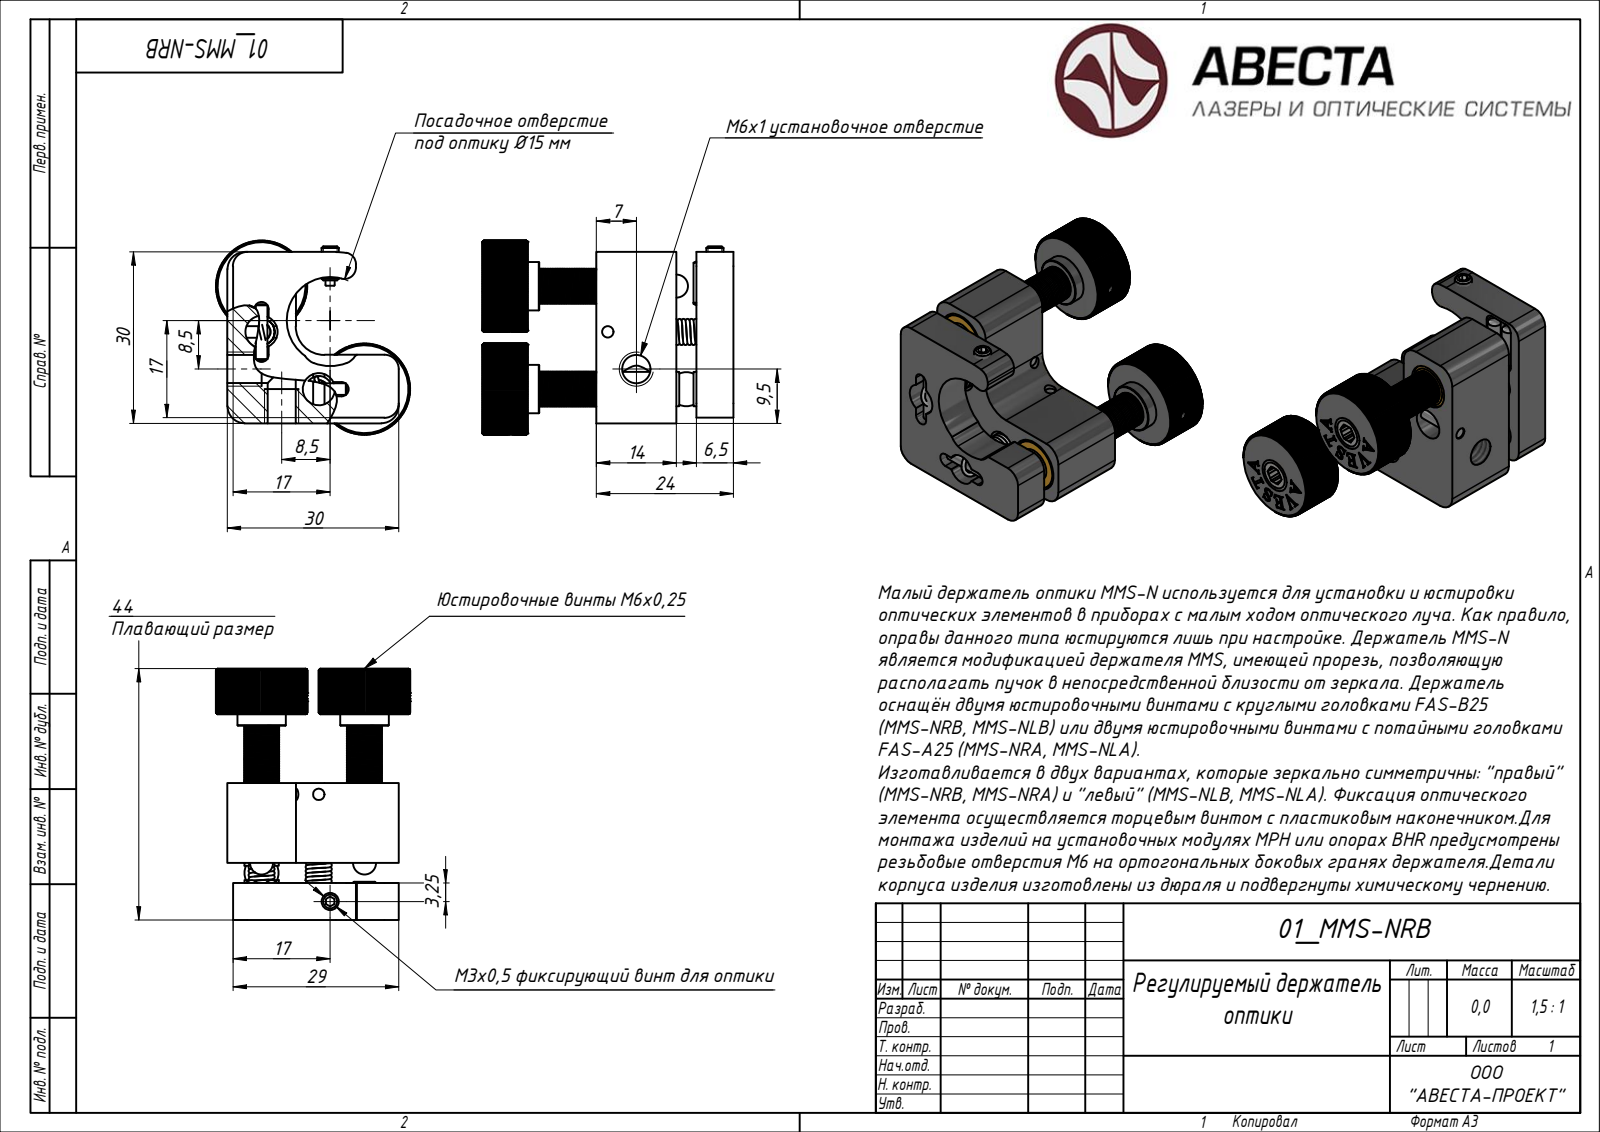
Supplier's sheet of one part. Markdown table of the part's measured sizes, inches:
| quantity | value |
| --- | --- |
| STEP written by | ST-DEVELOPER v15 (AUTOMOTIVE_DESIGN) |
| units | inches |
| bodies | 20 solids, 655 faces (294 planar, 0 cylindrical, 361 other) |
| overall size | 1.605 × 1.339 × 1.339 |
| volume | 0.858 in³ |
| surface area | 18.74 in² |
| main face-to-face distances | 0.394, 0.256, 0.945, 0.138, 0.472, 0.551, 0.039, 0.689, 0.433, 1.181 |
